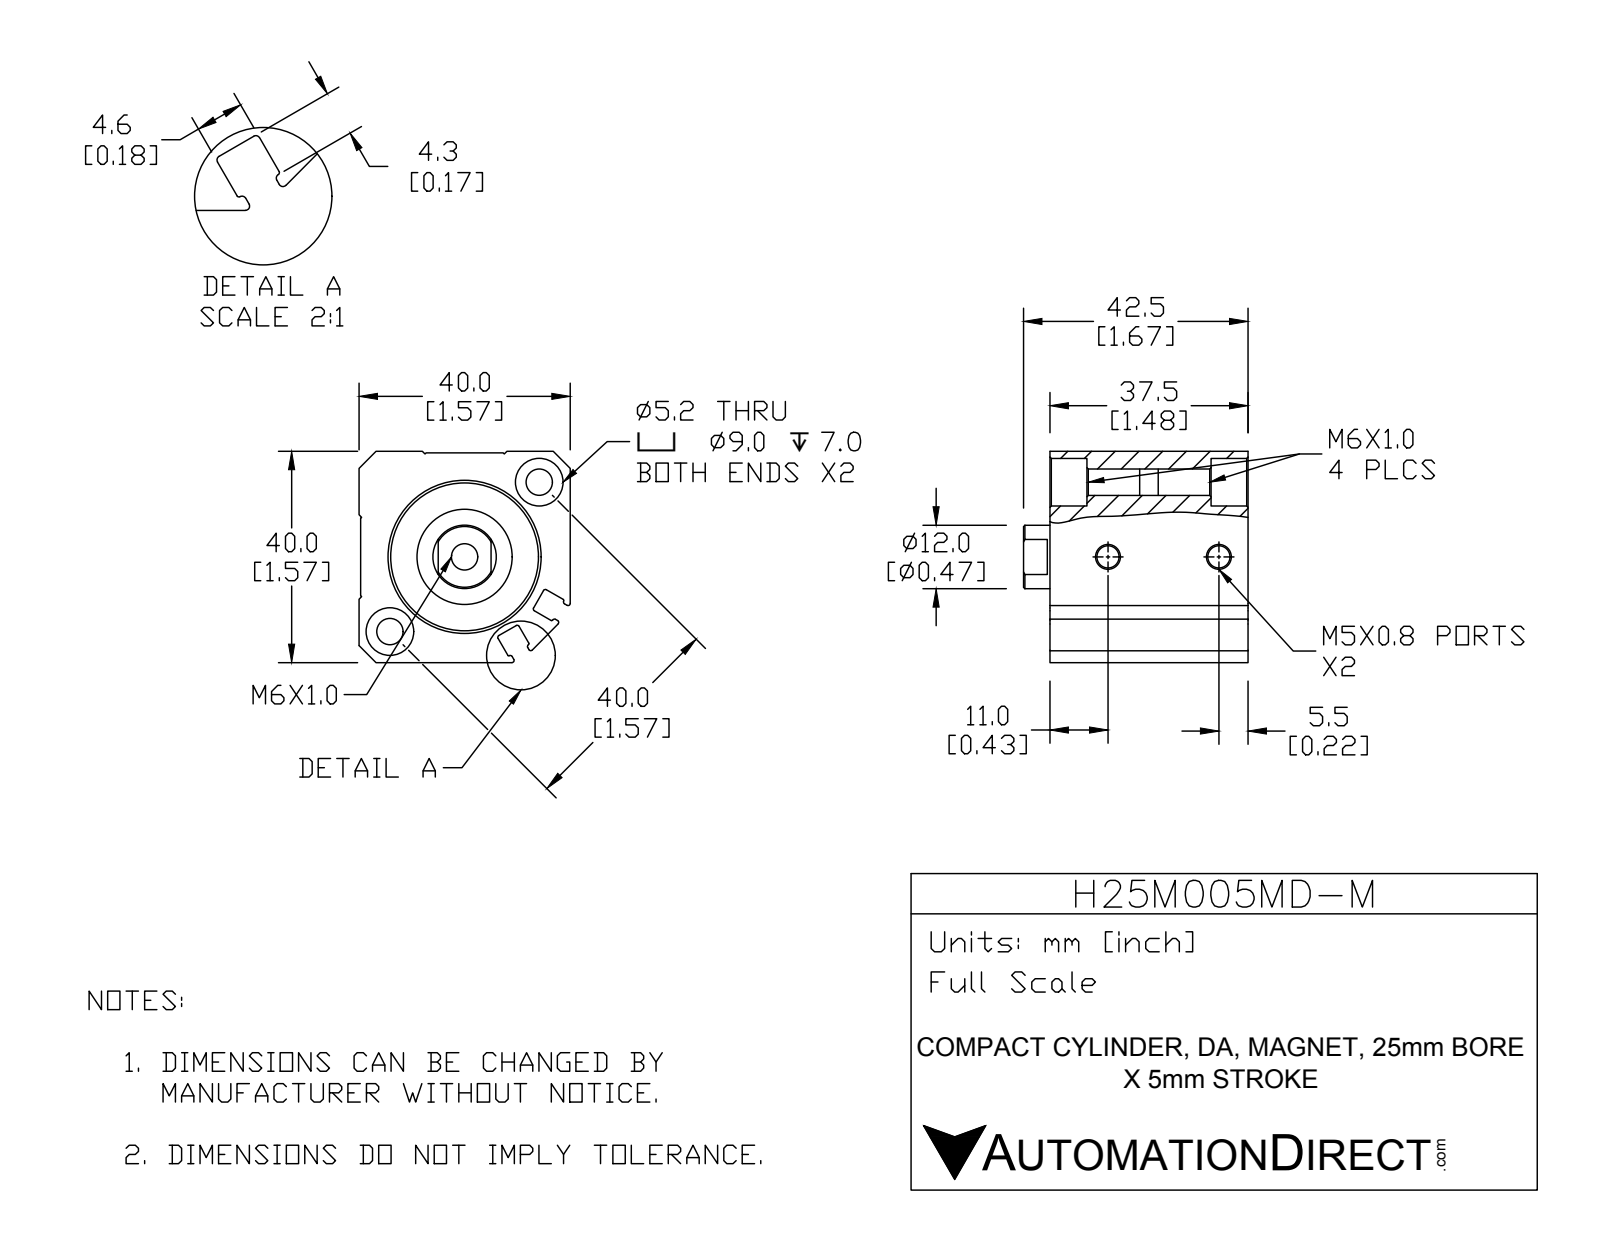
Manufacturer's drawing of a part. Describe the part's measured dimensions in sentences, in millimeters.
The part is named "H25M005MD-M; H25M005MD-M-PISTON; H25M005MD-M-BODY". Its 3-D file was written by "SolidWorks 2015 (CONFIG_CONTROL_DESIGN)". It is 2 solids with 141 faces: 53 planar, 55 cylindrical and 33 other. Overall it measures 42.5 by 40 by 40 millimeters. Its volume is 48 681 cubic millimeters and its surface area 17 807 square millimeters. Round holes: 3 of diameter 5, 2 of diameter 4.2, 2 of diameter 9, 1 of diameter 12, 1 of diameter 16, 1 of diameter 25, 1 of diameter 28. Round bosses or shafts: 1 of diameter 18, 1 of diameter 14. Partial cylindrical surfaces (rounded edges, fillets, slot ends): 12 of radius 0.4, 4 of radius 0.2. The main face-to-face distances are 40, 39.7, 4, 37.5, 33.5, 1.4, 2.6, 36.1, 26.5, 5.5. The hole center spacings are 20, 21, 39.99.
